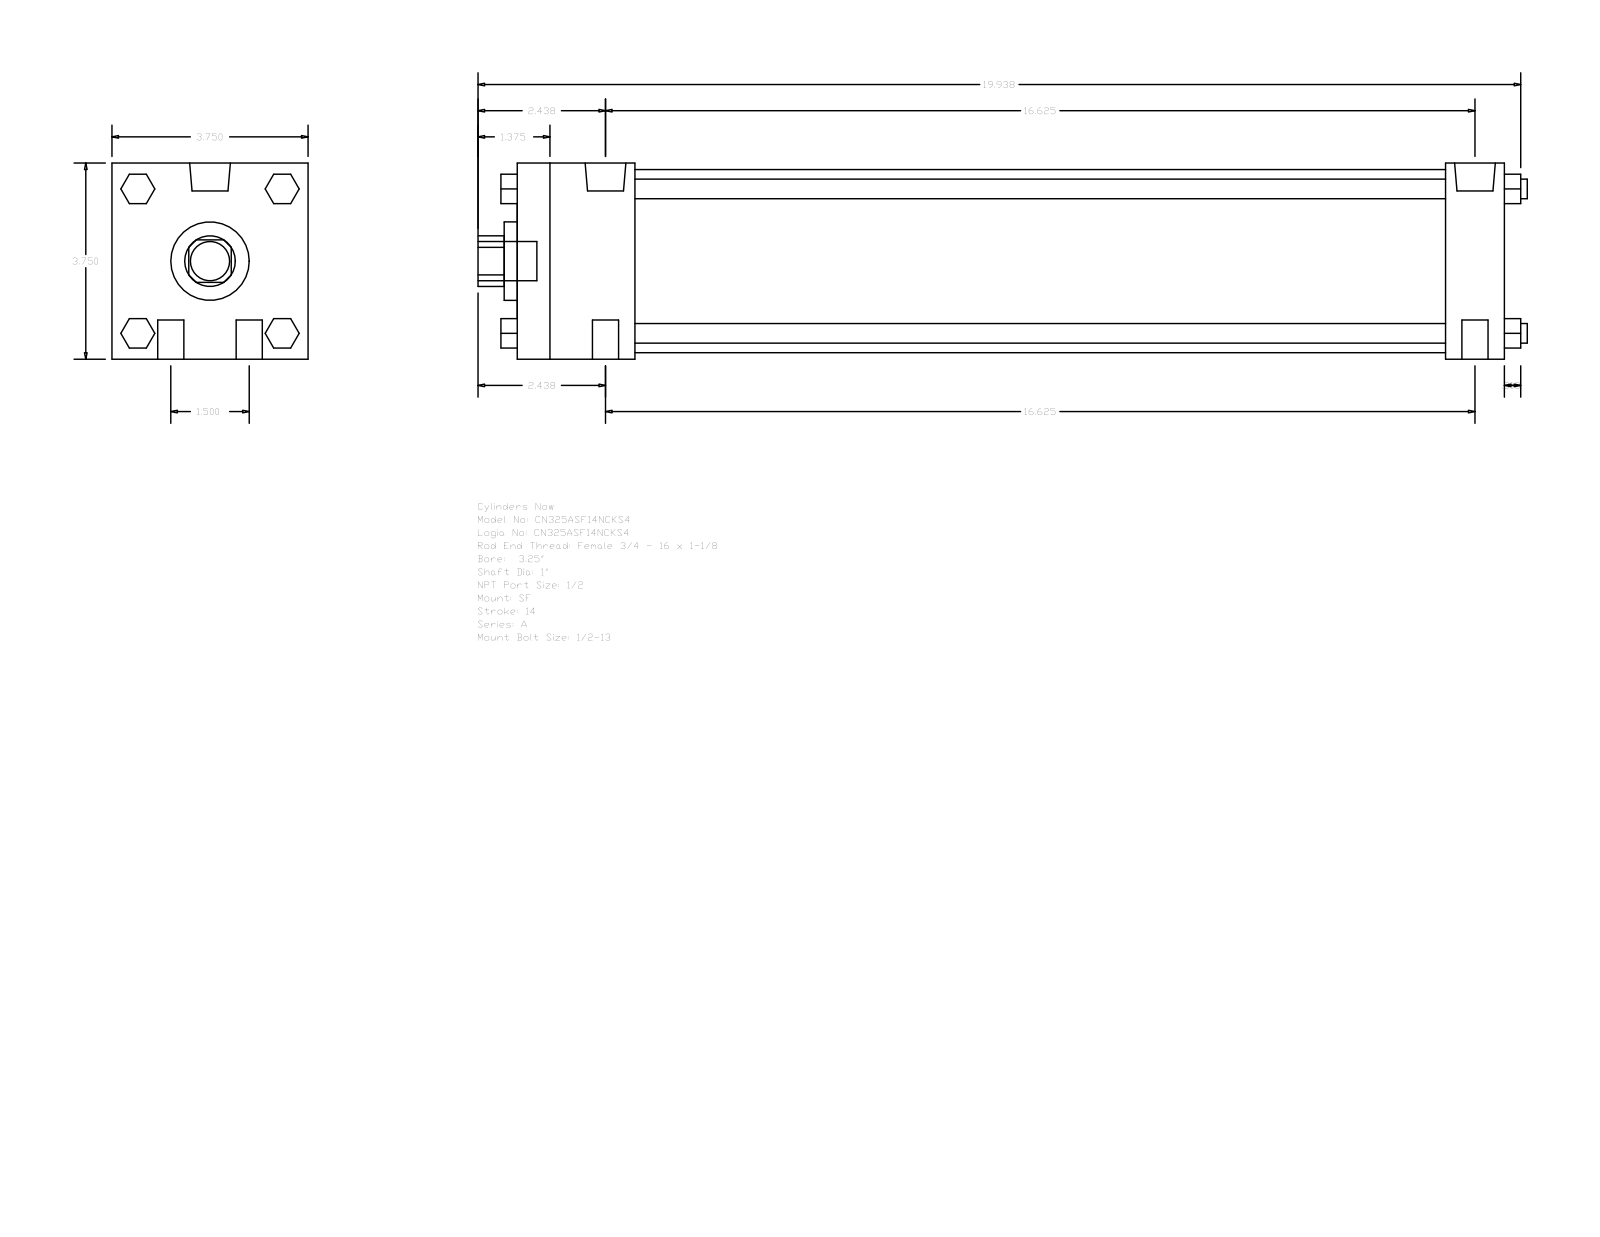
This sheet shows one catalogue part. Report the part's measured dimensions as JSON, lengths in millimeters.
{"part_name": "A_SF__0325_1", "step_written_by": "GSSL Pune (CONFIG_CONTROL_DESIGN)", "units": "millimeters", "bodies": {"solids": 0, "faces": 124, "planar": 94, "cylindrical": 30, "other": 0}, "overall_size": [509.59, 95.25, 95.25], "round_holes": [[25.4, 1], [38.1, 1], [88.9, 1]], "round_bosses_or_shafts": [[12.7, 4], [9.53, 4], [19.77, 2], [8.73, 2], [19.05, 1]], "partial_cylinders_radius": [[12.29, 1]], "face_to_face_distances": [95.24, 479.43, 450.85, 28.58, 57.15, 393.7, 422.28, 14.28, 35.05, 60.71]}
